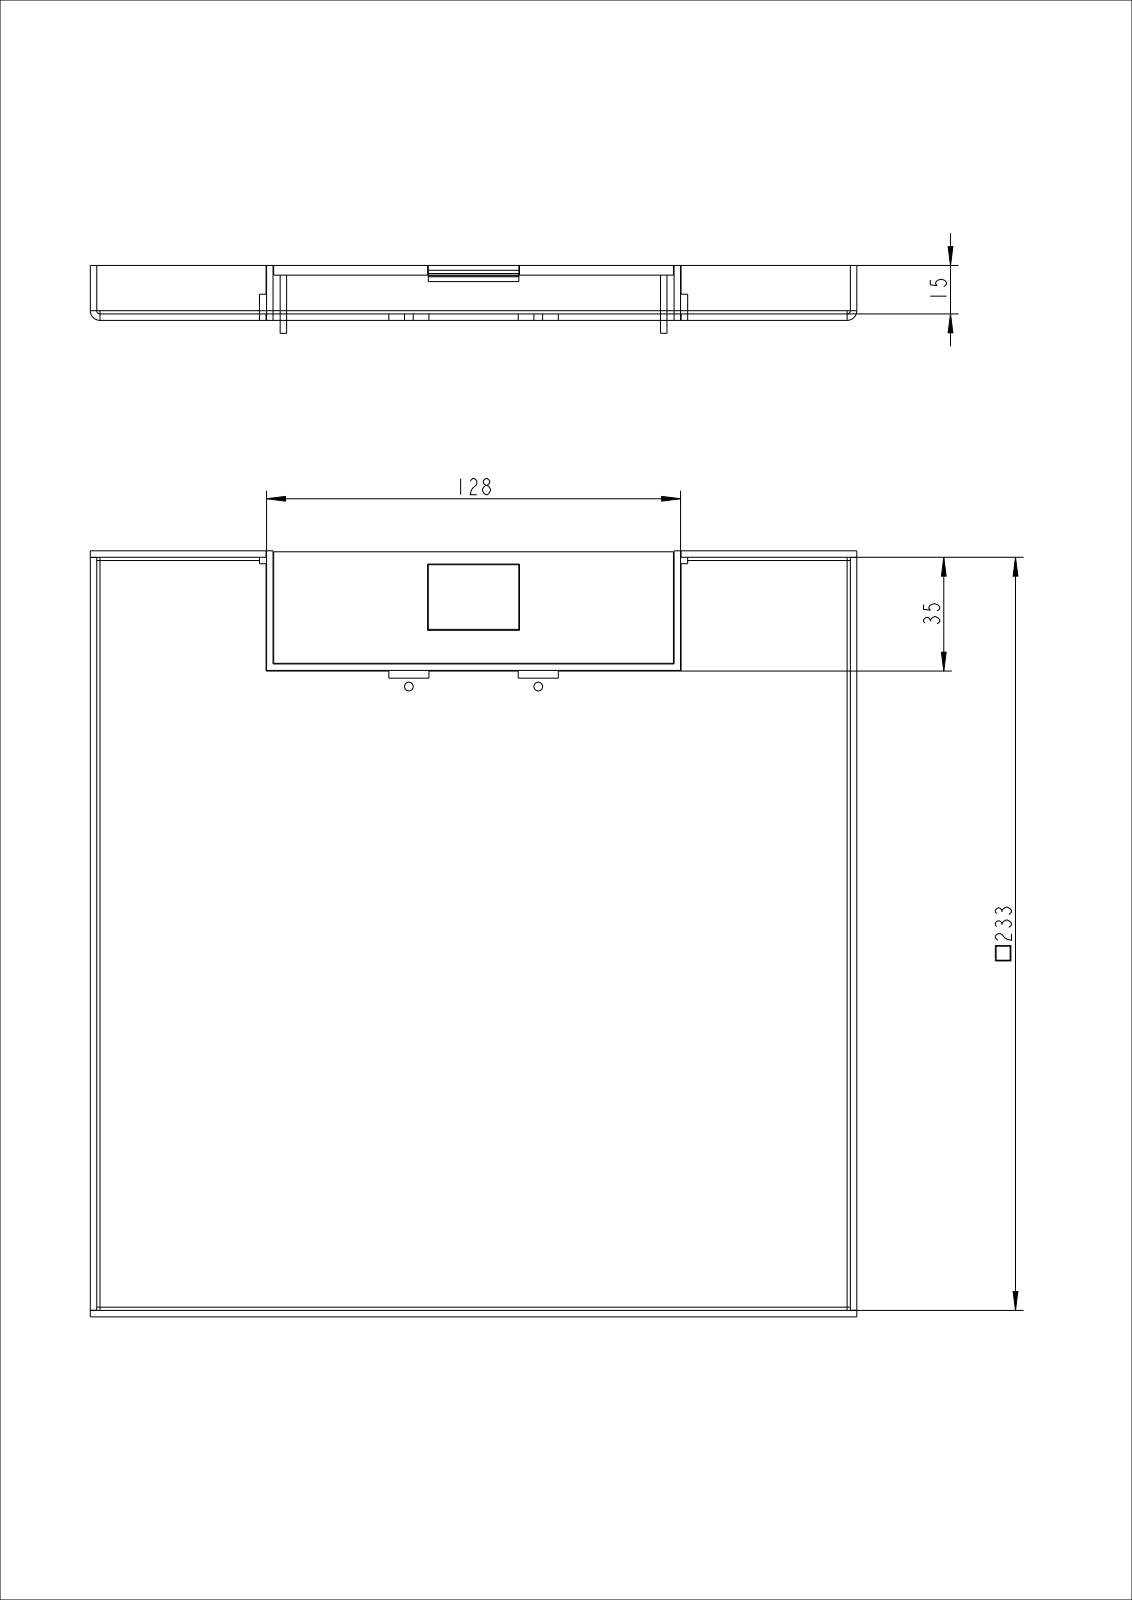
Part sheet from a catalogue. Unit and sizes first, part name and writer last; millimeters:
Units: millimetres
Overall size (bounding box): 237 × 237 × 21
Round holes (diameter × count): ⌀2.7 ×2
Partial cylindrical surfaces — rounded edges, fillets, slot ends (radius × count): R1 ×4, R3 ×4, R6.6 ×1
Main face-to-face distances: 2, 235, 17, 15, 237, 233, 200, 12, 14, 3
Hole centre spacings: 40
Volume: 147 371 mm³ · Surface area: 148 131 mm²
Bodies: 4 solids, 119 faces (104 planar, 15 cylindrical, 0 other)
Part name (STEP PRODUCT): T-00612; T-00622S; T-00621S; T-00724S (+3 more)
STEP written by: CREO PARAMETRIC BY PTC INC, 2022024 (AUTOMOTIVE_DESIGN)
